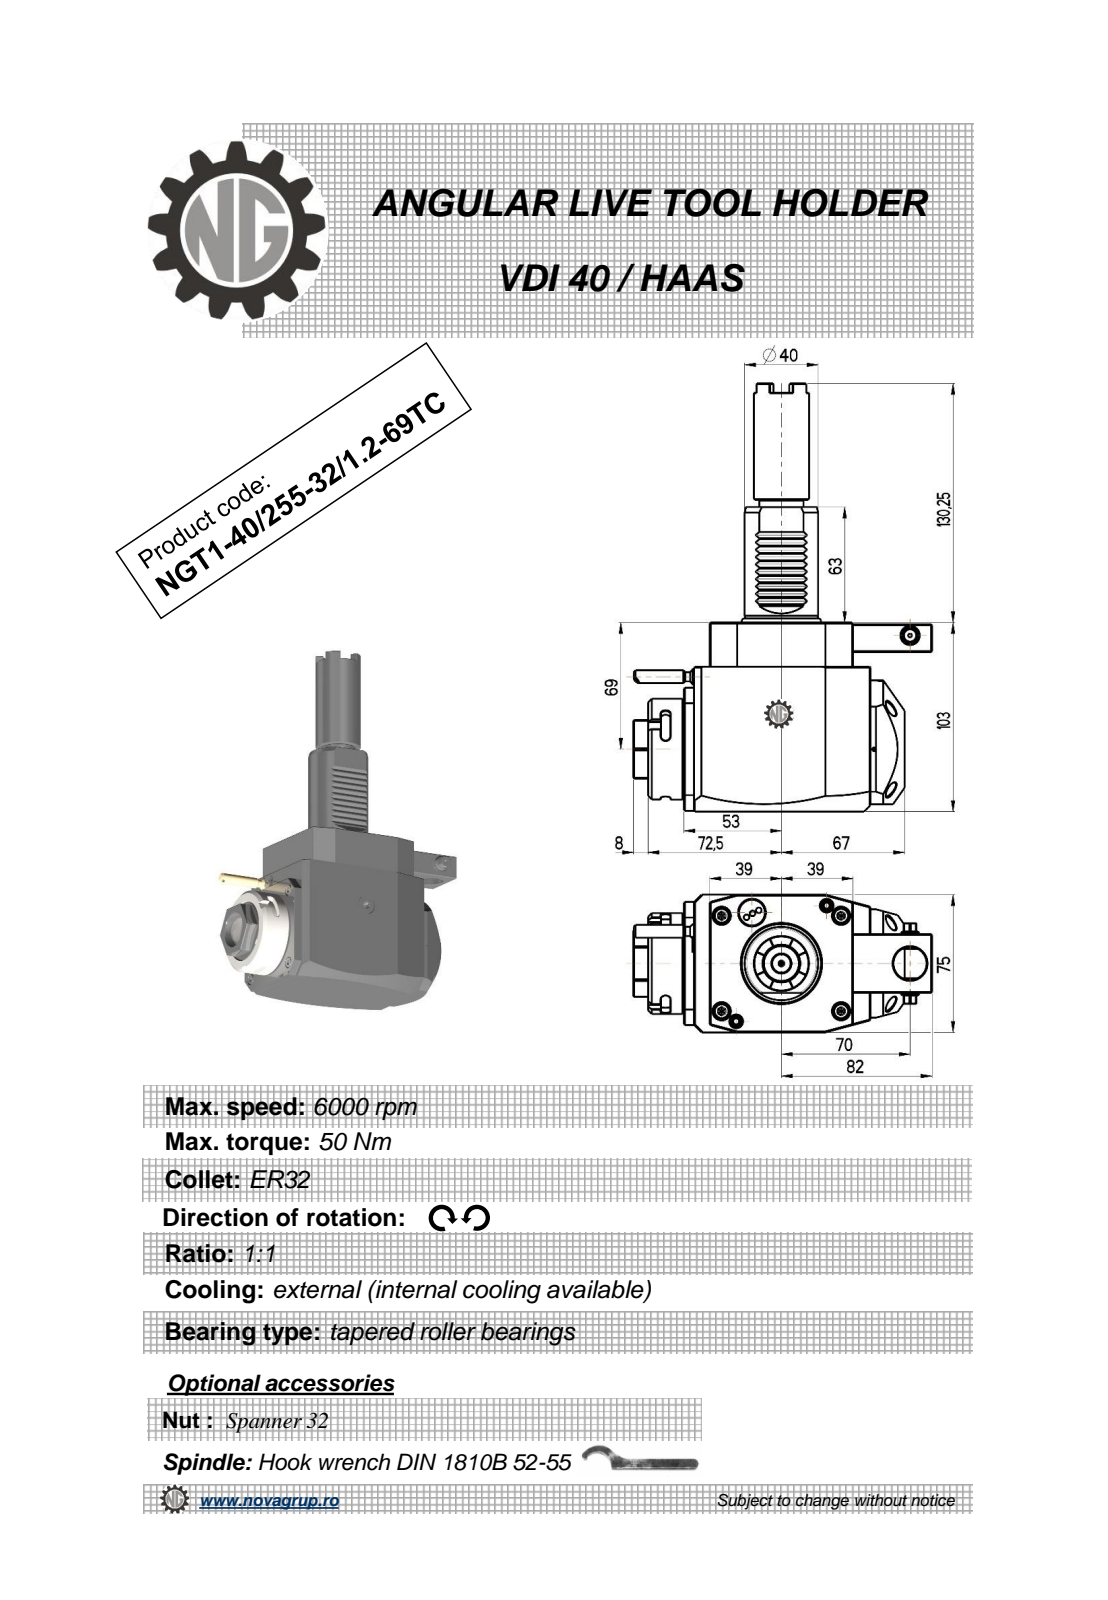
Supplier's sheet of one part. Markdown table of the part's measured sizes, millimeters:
| quantity | value |
| --- | --- |
| part name | NGT1_40_255_32_1_2_69TC |
| STEP written by | PRO/ENGINEER BY PARAMETRIC TECHNOLOGY CORPORATION, 2010280 (CONFIG_CONTROL_DESIGN) |
| units | millimeters |
| bodies | 1 solid, 387 faces (219 planar, 80 cylindrical, 88 other) |
| overall size | 233.25 × 162.5 × 75 |
| volume | 946 350 mm³ |
| surface area | 77 531 mm² |
| round holes (diameter × count) | 2 × 1, 2.5 × 1, 3 × 1, 9.5 × 1, 18 × 1, 20 × 1, 23 × 1 |
| round bosses / shafts (diameter × count) | 8.96 × 2, 55 × 1, 48 × 1, 40 × 1, 30 × 1, 24 × 1, 10 × 1, 7 × 1 |
| partial cylindrical surfaces (radius × count) | 0.3 × 10, 2.5 × 6, 180 × 2, 0.5 × 1, 3.85 × 1, 4.25 × 1, 24.5 × 1, 37.5 × 1 |
| main face-to-face distances | 75, 103, 33.5, 19.5, 79, 8, 14, 102, 21.5, 87 |
| hole center spacings | 28.11, 43.2, 61.5, 70 |
